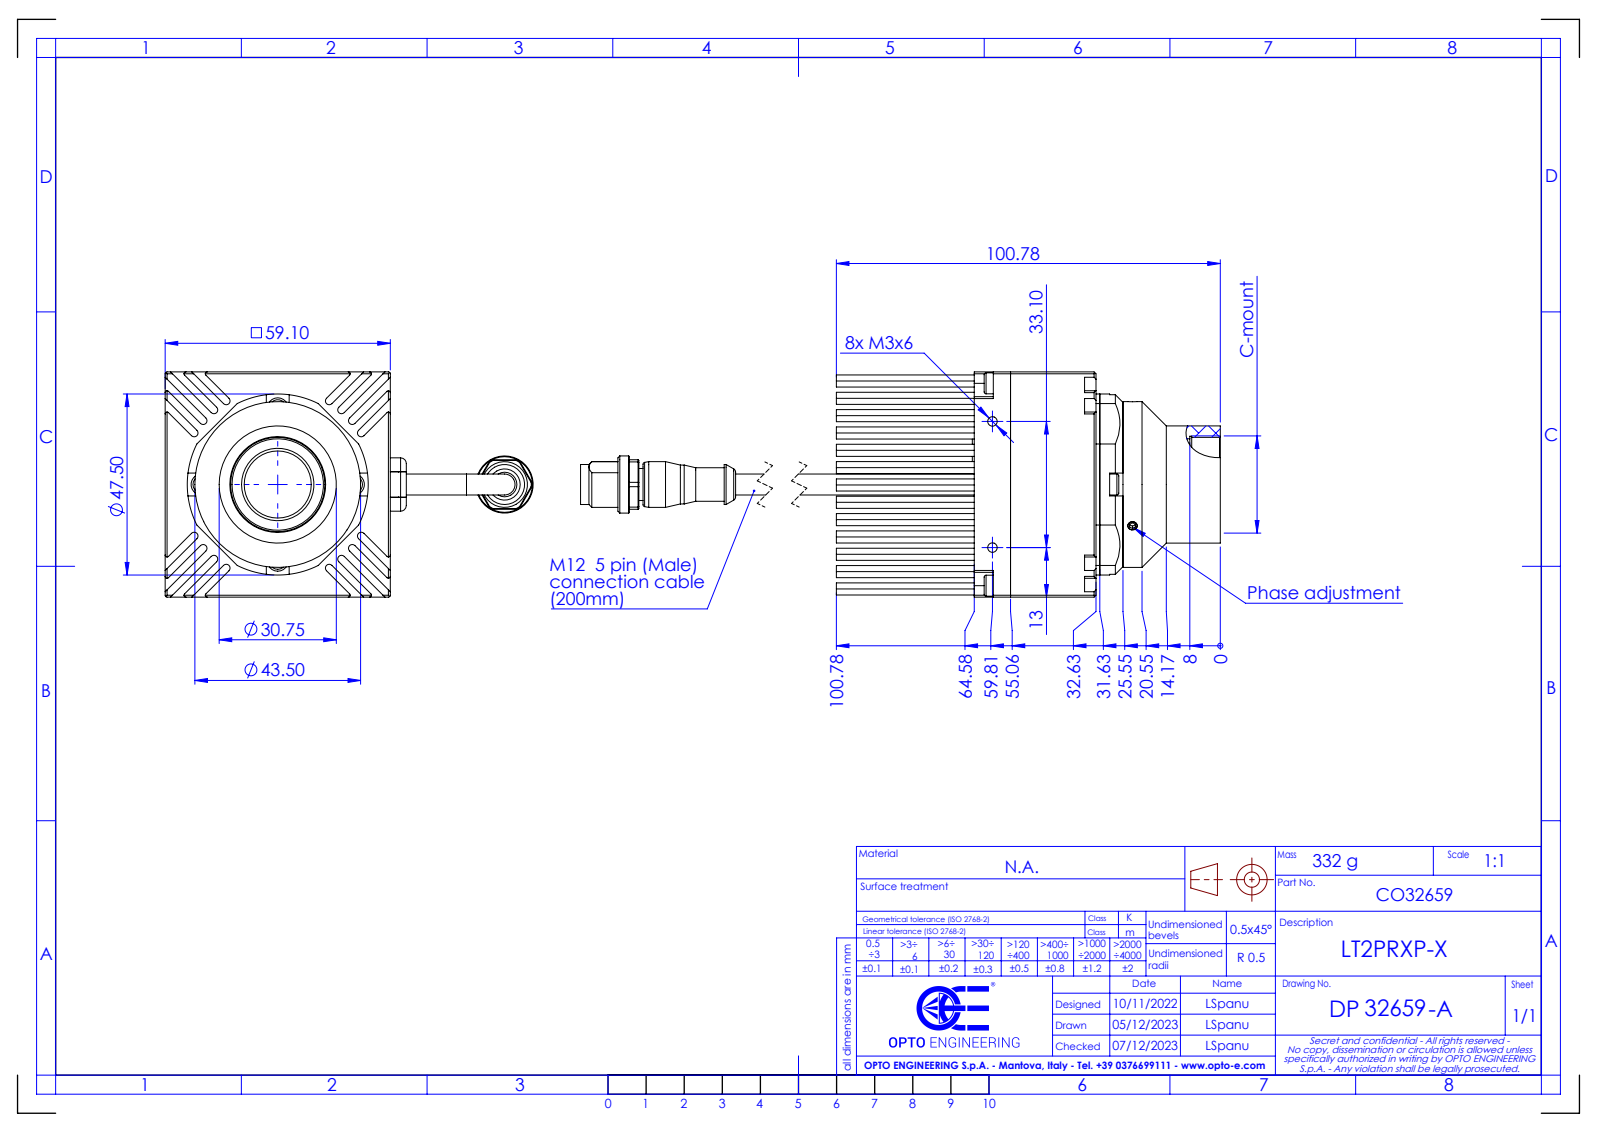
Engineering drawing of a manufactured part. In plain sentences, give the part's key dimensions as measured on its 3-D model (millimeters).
The part is named "DP32659-A_LT2PRXP-X". Its 3-D file was written by "SolidWorks 2021 (CONFIG_CONTROL_DESIGN)". It is 0 solids with 663 faces: 342 planar, 278 cylindrical and 43 other. Overall it measures 202.96 by 96.6 by 59.1 millimeters. Round holes: 7 of diameter 2.5, 1 of diameter 3.5, 1 of diameter 8.3, 1 of diameter 19, 1 of diameter 24, 1 of diameter 24.75, 1 of diameter 25.35. Round bosses or shafts: 80 of diameter 3.18, 10 of diameter 5.5, 5 of diameter 1, 1 of diameter 43.5, 1 of diameter 30.75, 1 of diameter 15, 1 of diameter 14.2, 1 of diameter 12. Partial cylindrical surfaces (rounded edges, fillets, slot ends): 28 of radius 0.5, 16 of radius 1, 4 of radius 3.5, 2 of radius 1.5, 1 of radius 0.6, 1 of radius 7.2, 1 of radius 23.75. The main face-to-face distances are 59.1, 31.96, 2, 68.15, 36.19, 7.08, 39.04, 75.23, 3.95, 5.95. The hole center spacings are 33.1, 40.31, 11.27, 35.4, 59.55.
